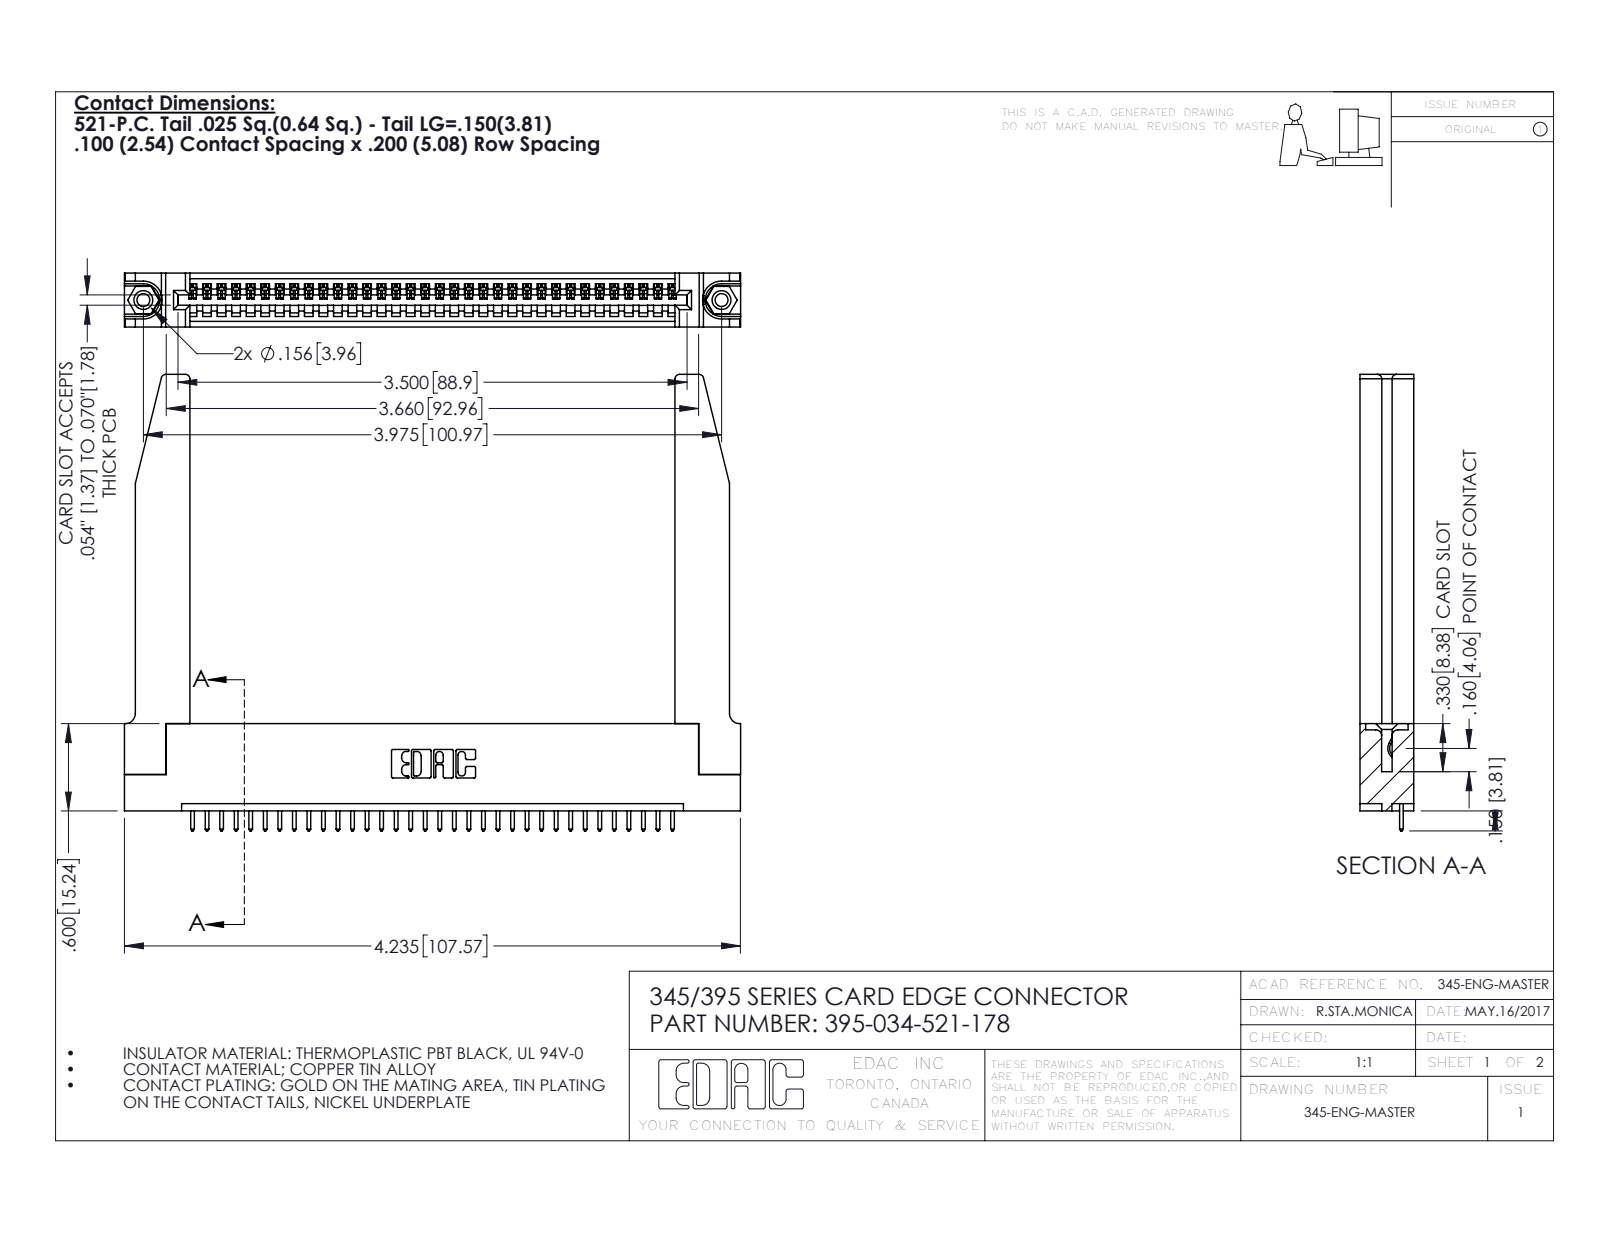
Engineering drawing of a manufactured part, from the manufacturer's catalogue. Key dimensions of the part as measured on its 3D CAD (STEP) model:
Part name (STEP PRODUCT): 395-034-521-178; 345-220-078_345-220-078; 345-250-001_345-250-001-102; 345 Part_Flush Mounting Lugs - 0.156 Dia-TH (+1 more)
STEP written by: SolidWorks 2016 (CONFIG_CONTROL_DESIGN)
Units: inches
Bodies: 39 solids, 2332 faces (1582 planar, 698 cylindrical, 52 other)
Overall size (bounding box): 4.236 × 3.137 × 0.37
Volume: 1.088 in³ · Surface area: 30.57 in²
Round holes (diameter × count): ⌀0.089 ×2, ⌀0.125 ×2, ⌀0.156 ×2, ⌀0.064 ×1
Round bosses / shafts (diameter × count): ⌀0.155 ×2
Partial cylindrical surfaces — rounded edges, fillets, slot ends (radius × count): R0.006 ×68, R0.01 ×68, R0.01 ×22, R0.03 ×8, R0.007 ×6, R0.031 ×6, R0.026 ×3, R0.031 ×2
Main face-to-face distances: 0.37, 0.072, 0.298, 0.2, 0.098, 0.272, 0.025, 0.225, 0.15, 0.148
Hole centre spacings: 0.27, 3.74, 3.975
